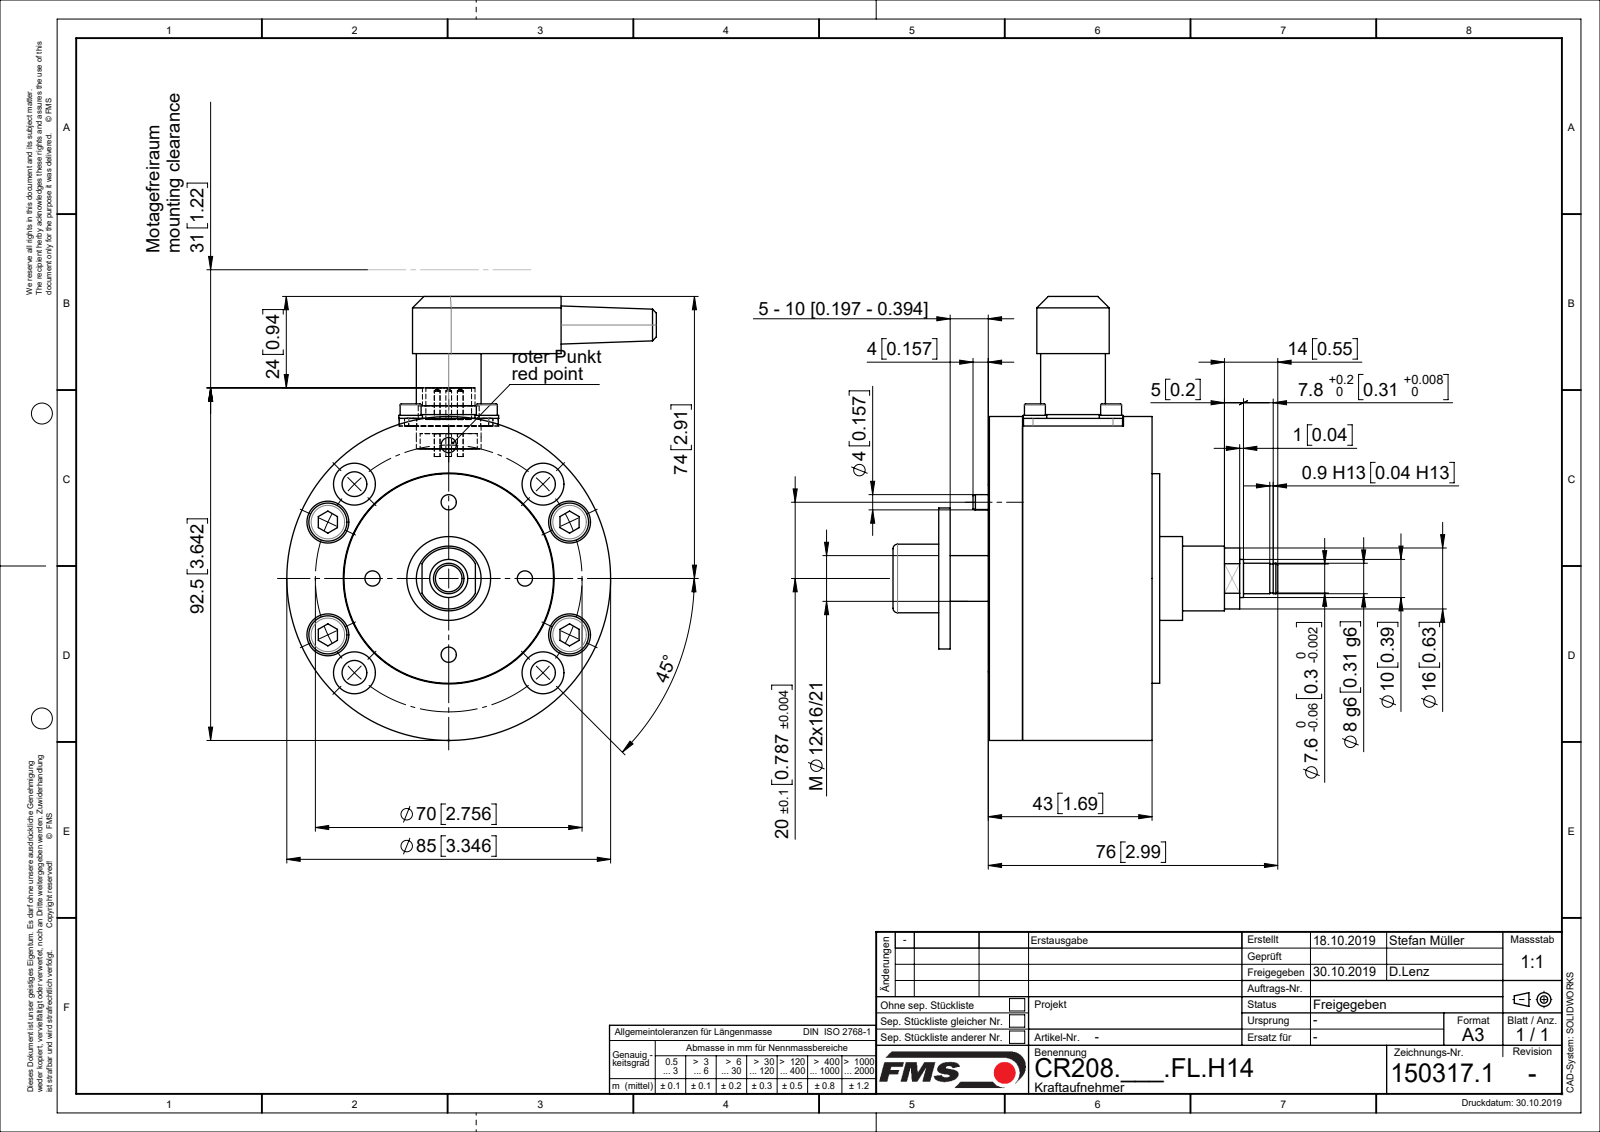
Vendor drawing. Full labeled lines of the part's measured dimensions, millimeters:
Part name (STEP PRODUCT): C1503171_STP; C0709081_STP; C0612056; C0709072 (+8 more)
STEP written by: Mechanical Desktop 2009 (CONFIG_CONTROL_DESIGN)
Units: millimetres
Bodies: 25 solids, 484 faces (155 planar, 242 cylindrical, 87 other)
Overall size (bounding box): 116.5 × 101.9 × 97
Volume: 218 652 mm³ · Surface area: 79 018 mm²
Round holes (diameter × count): ⌀6.5 ×8, ⌀11 ×8, ⌀2 ×5, ⌀2.6 ×4, ⌀3.2 ×4, ⌀4 ×4, ⌀5.15 ×4, ⌀7 ×4, ⌀7.15 ×1, ⌀10.68 ×1, ⌀12 ×1, ⌀13 ×1
Round bosses / shafts (diameter × count): ⌀10 ×5, ⌀1.5 ×5, ⌀6.2 ×4, ⌀6 ×4, ⌀5.5 ×4, ⌀5 ×4, ⌀3 ×4, ⌀17 ×2
Partial cylindrical surfaces — rounded edges, fillets, slot ends (radius × count): R2.5 ×4, R5 ×2, R8 ×1, R9.5 ×1
Main face-to-face distances: 8.6, 34, 2, 42.6, 45, 16, 36, 33.5, 8, 44.6
Hole centre spacings: 20, 25.2, 35, 51.14, 28.28, 12.16, 14.14, 18.87
